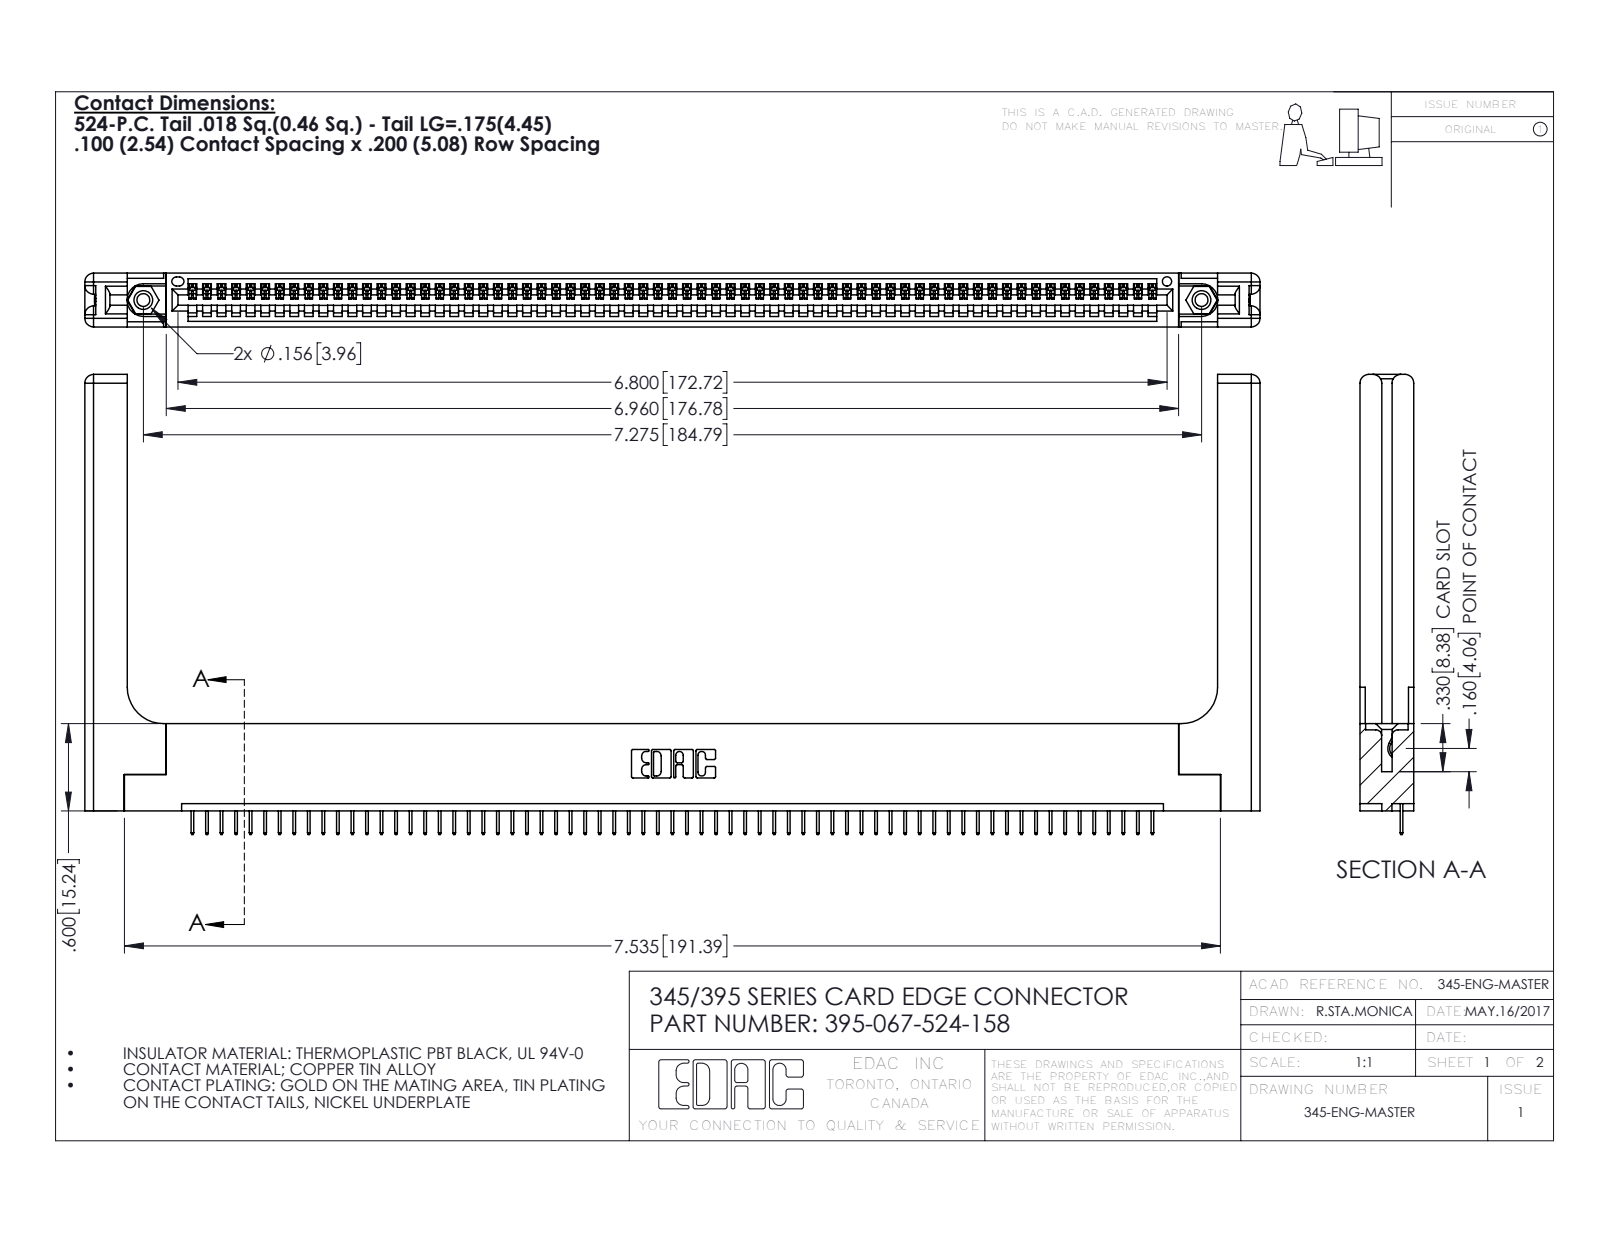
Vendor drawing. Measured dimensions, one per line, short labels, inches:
name: 395-067-524-158; 345-220-058_345-220-058; 345-292-001_345-293-124; 345 Part_Flush Mounting Lugs - 0.156 Dia-TH (+1 more)
written by: SolidWorks 2016 (CONFIG_CONTROL_DESIGN)
unit: in
bodies: 72 solids, 4536 faces (3310 planar, 1166 cylindrical, 60 other)
size: 8.079 × 3.162 × 0.37
volume: 1.705 in³; area: 47.46 in²
holes: 2× ⌀0.089, 2× ⌀0.125, 2× ⌀0.156, 1× ⌀0.064
bosses: 2× ⌀0.155
rounds: 134× R0.006, 22× R0.01, 16× R0.06, 6× R0.007, 6× R0.031, 3× R0.026, 2× R0.03, 2× R0.031
face distances: 0.072, 0.37, 0.298, 0.2, 0.098, 0.272, 0.025, 0.225, 0.148, 0.15
hole spacings: 0.27, 7.039, 7.275
